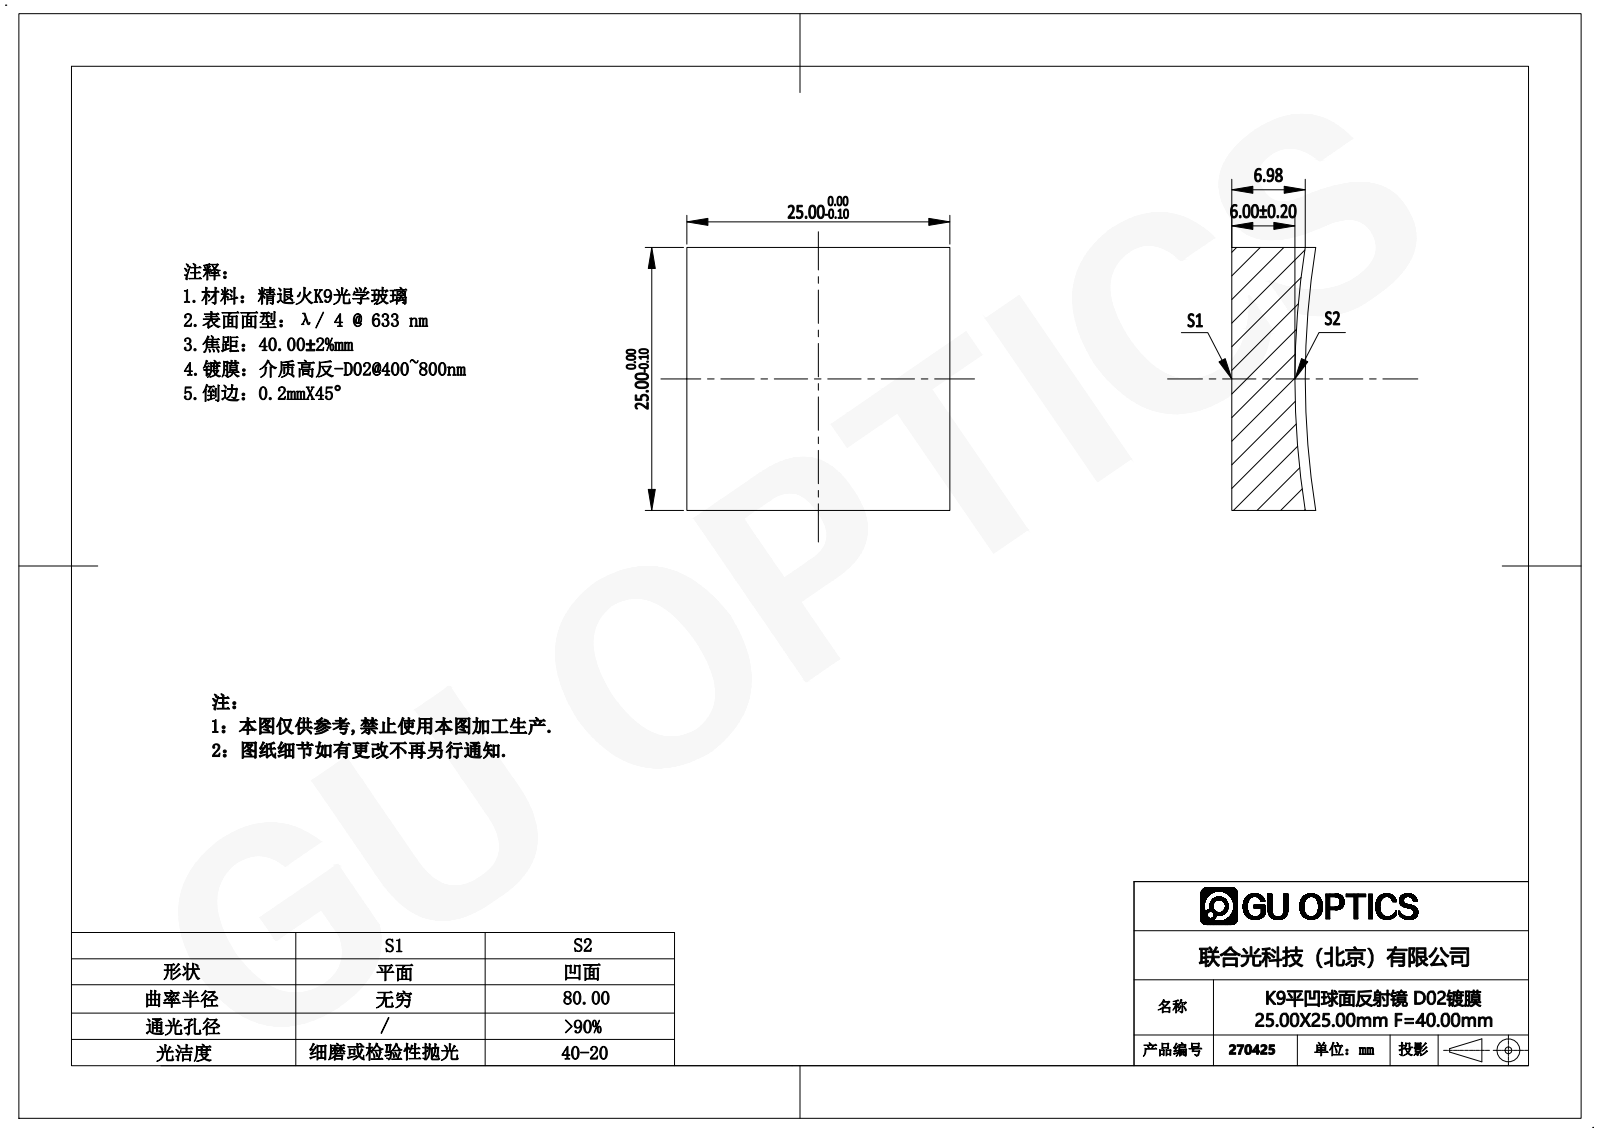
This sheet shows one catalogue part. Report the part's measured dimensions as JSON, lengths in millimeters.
{"part_name": "270035", "step_written_by": "SolidWorks 2019 (AUTOMOTIVE_DESIGN)", "units": "millimeters", "bodies": {"solids": 1, "faces": 7, "planar": 5, "cylindrical": 0, "other": 2}, "overall_size": [25, 25, 7.98], "volume_mm3": 4159, "surface_area_mm2": 1987, "face_to_face_distances": [25]}
